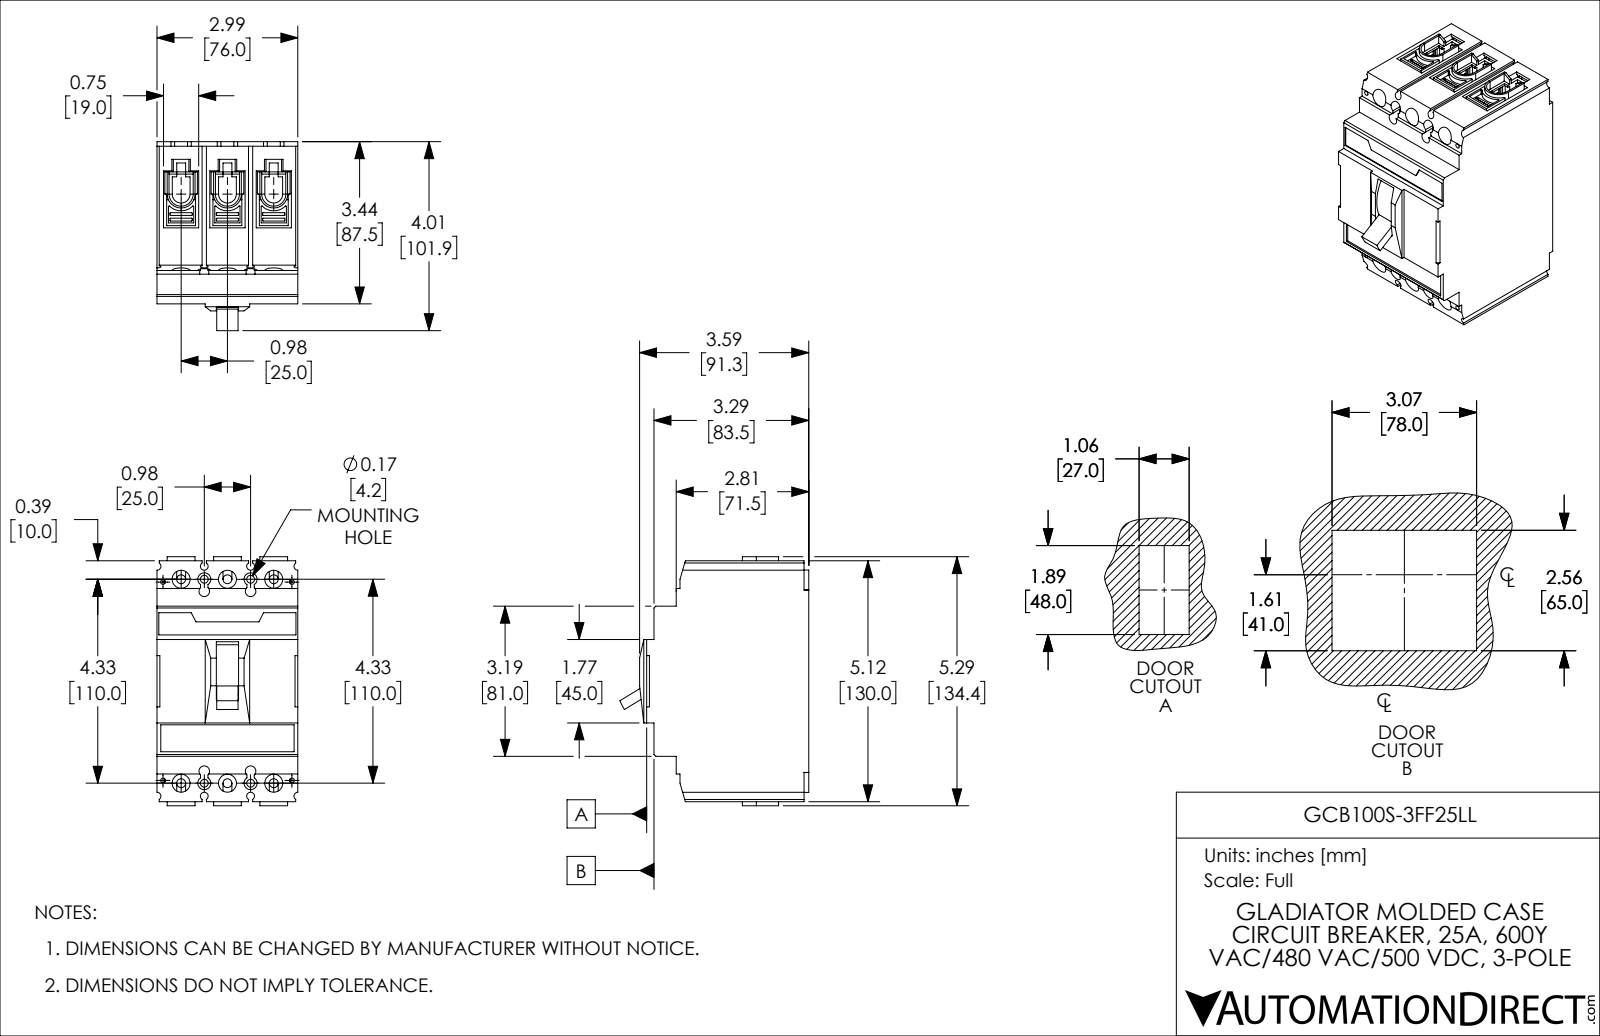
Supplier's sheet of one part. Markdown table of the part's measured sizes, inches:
| quantity | value |
| --- | --- |
| part name | GCB100S-3FF25LL |
| STEP written by | SolidWorks 2021 (CONFIG_CONTROL_DESIGN) |
| units | inches |
| bodies | 1 solid, 1256 faces (784 planar, 424 cylindrical, 48 other) |
| overall size | 5.291 × 4.013 × 2.992 |
| volume | 43.23 in³ |
| surface area | 148.5 in² |
| round holes (diameter × count) | 0.165 × 8, 0.189 × 6, 0.382 × 6, 0.098 × 4, 0.276 × 4 |
| partial cylindrical surfaces (radius × count) | 0.012 × 86, 0.02 × 38, 0.039 × 14, 0.157 × 14, 0.024 × 6, 0.083 × 4, 0.112 × 4, 0.189 × 3 |
| main face-to-face distances | 2.992, 0.984, 0.622, 4.496, 1.732, 0.11, 3.445, 0.748, 1.969, 5.118 |
| hole center spacings | 0.492, 0.564, 0.984, 4.359, 4.633, 4.441, 4.331, 0.276 |
